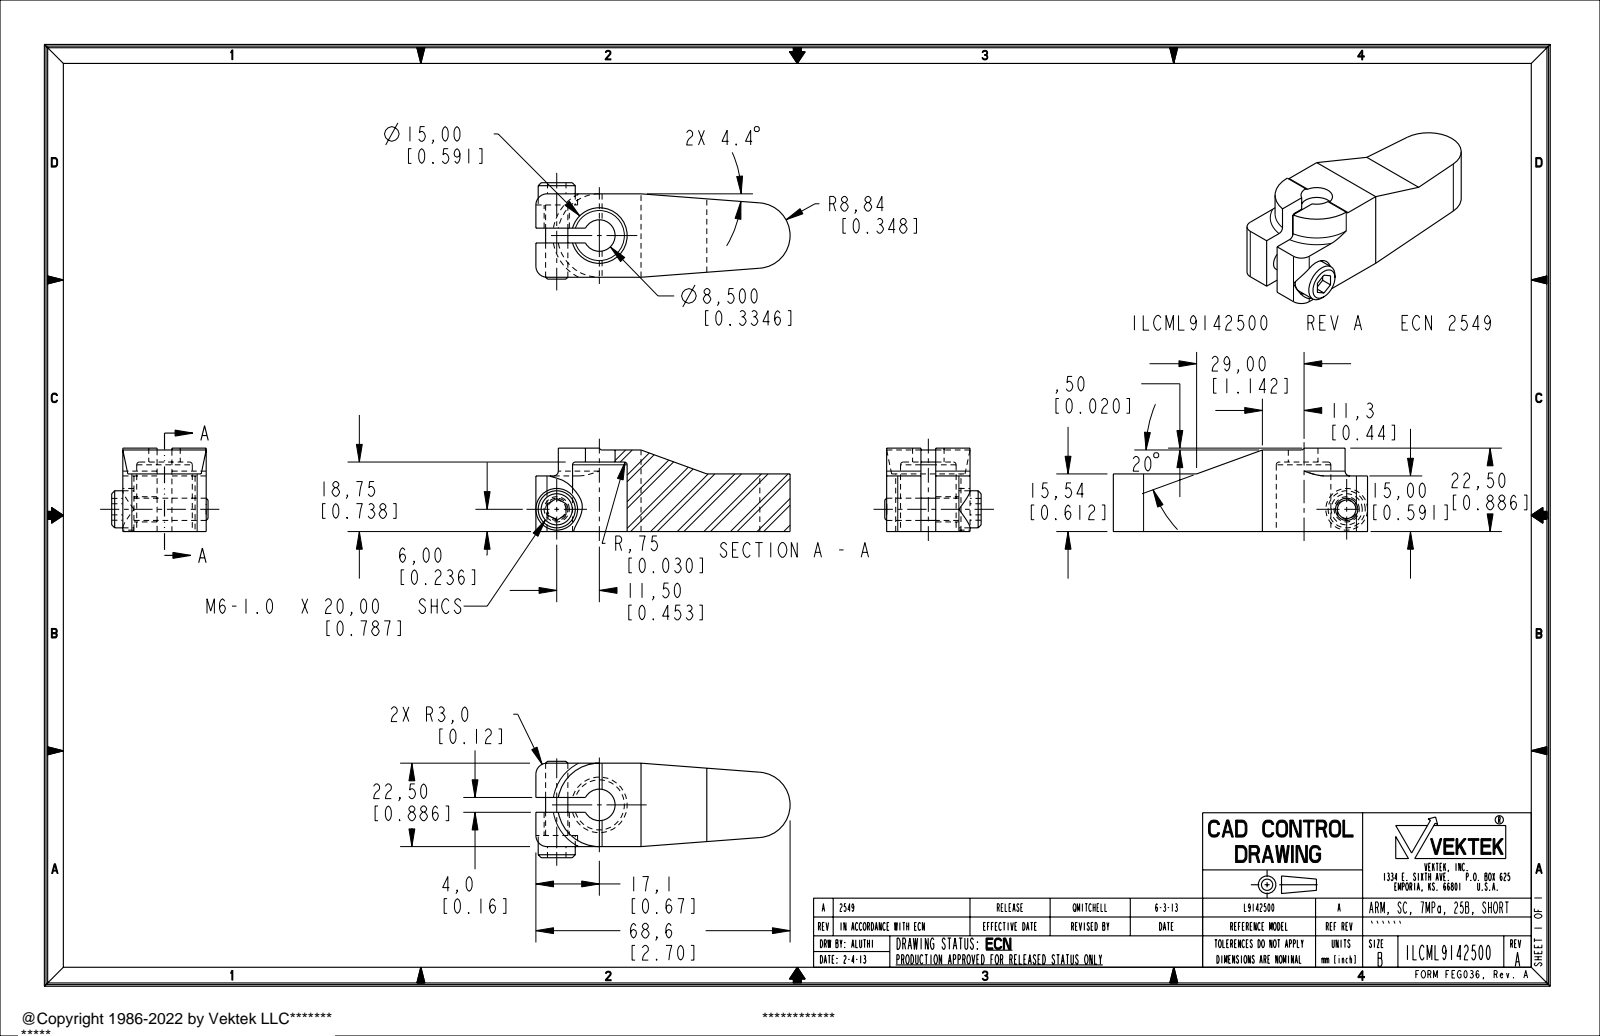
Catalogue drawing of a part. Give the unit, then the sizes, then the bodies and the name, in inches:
Units: inches
Overall size (bounding box): 2.701 × 1.024 × 0.886
Round holes (diameter × count): ⌀0.268 ×1, ⌀0.335 ×1, ⌀0.443 ×1, ⌀0.591 ×1
Round bosses / shafts (diameter × count): ⌀0.394 ×1, ⌀0.236 ×1
Partial cylindrical surfaces — rounded edges, fillets, slot ends (radius × count): R0.118 ×2, R0.031 ×1, R0.348 ×1, R0.443 ×1
Main face-to-face distances: 0.886, 0.612, 0.364, 0.522, 0.866, 0.254, 0.02, 0.157, 0.148, 0.274
Volume: 1.323 in³ · Surface area: 11.77 in²
Bodies: 1 solid, 56 faces (28 planar, 21 cylindrical, 7 other)
Part name (STEP PRODUCT): ILCML9142500
STEP written by: PRO/ENGINEER BY PARAMETRIC TECHNOLOGY CORPORATION, 2007460 (AUTOMOTIVE_DESIGN_CC2)
